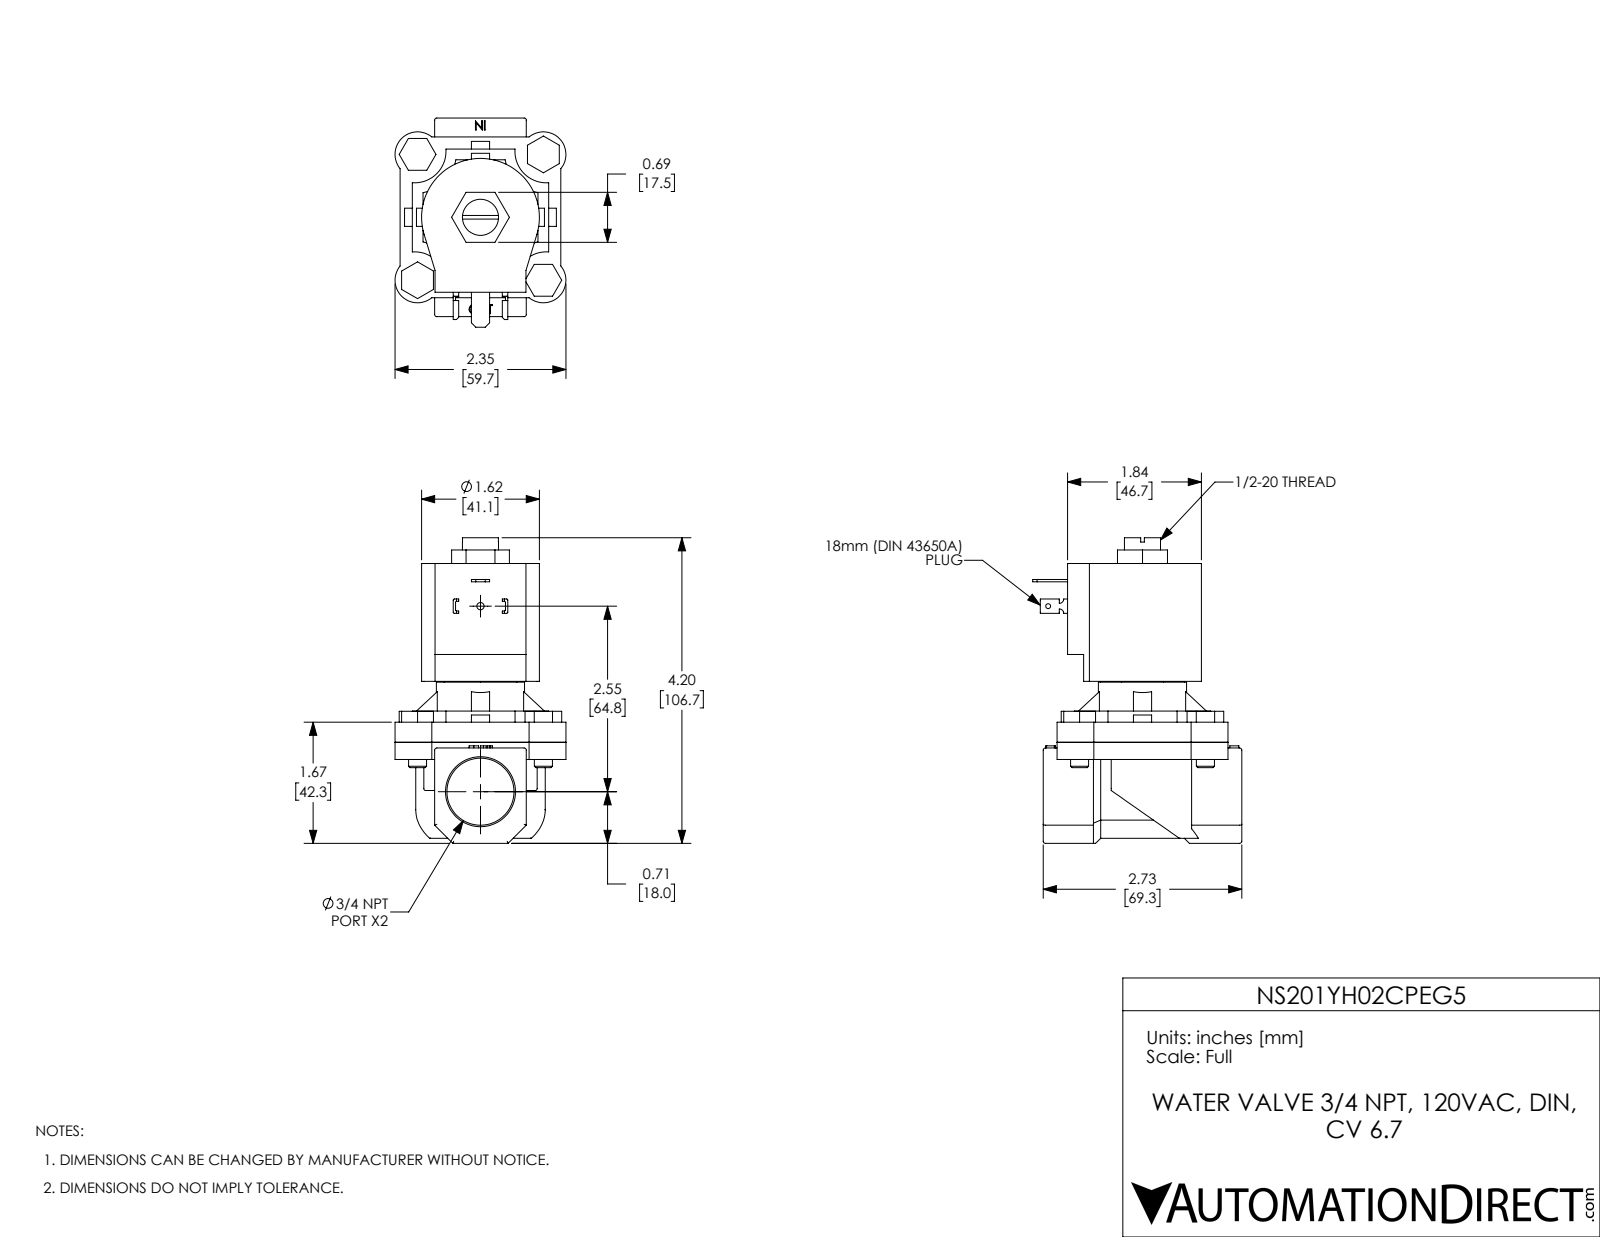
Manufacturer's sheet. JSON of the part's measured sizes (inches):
{"part_name": "NS201YH02CPEG5", "step_written_by": "SolidWorks 2024 (CONFIG_CONTROL_DESIGN)", "units": "inches", "bodies": {"solids": 11, "faces": 387, "planar": 241, "cylindrical": 113, "other": 33}, "overall_size": [4.2, 2.875, 2.35], "volume_in3": 10.6, "surface_area_in2": 70.72, "round_holes": [[0.25, 4], [0.067, 1], [0.1, 1], [0.496, 1], [0.512, 1], [0.922, 1], [1.155, 1]], "round_bosses_or_shafts": [[0.248, 4], [1.213, 1]], "partial_cylinders_radius": [[0.03, 15], [0.015, 8], [0.31, 4], [0.432, 4], [0.579, 4], [0.06, 2], [0.81, 1], [0.89, 1]], "face_to_face_distances": [0.276, 2.457, 2.181, 0.236, 0.512, 2.693, 0.475, 1.735, 1.26, 2.21], "hole_center_spacings": [1.223, 1.73, 2.446, 2.55]}
